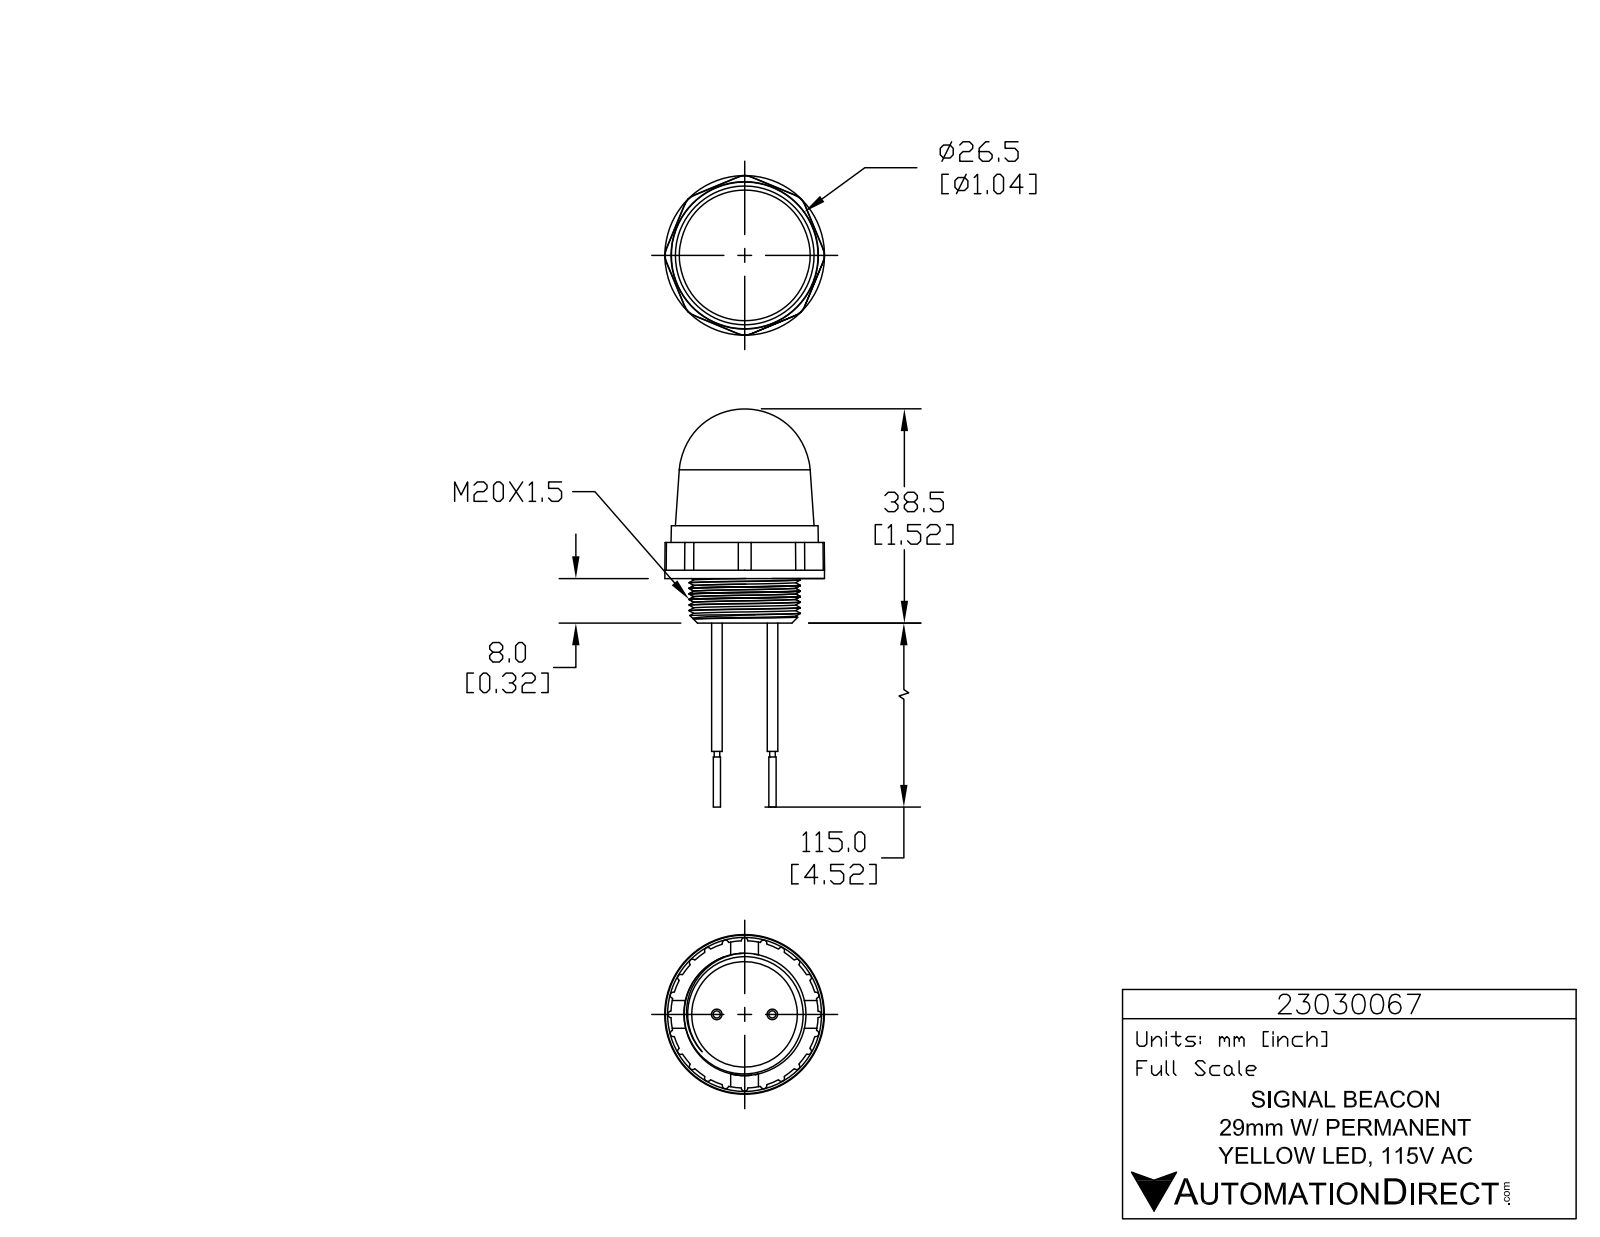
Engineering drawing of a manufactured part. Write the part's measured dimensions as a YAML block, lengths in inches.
part_name: "23030067"
step_written_by: "SolidWorks 2017 (AUTOMOTIVE_DESIGN)"
units: inches
bodies: {solids: 1, faces: 844, planar: 551, cylindrical: 203, other: 90}
overall_size: [2.82, 1.131, 1.131]
volume: 0.978
surface_area: 8.158
round_holes:
  - {diameter: 0.02, count: 3}
  - {diameter: 0.807, count: 1}
round_bosses_or_shafts:
  - {diameter: 0.113, count: 3}
  - {diameter: 0.028, count: 3}
  - {diameter: 0.075, count: 2}
  - {diameter: 0.051, count: 2}
  - {diameter: 0.039, count: 2}
  - {diameter: 1.131, count: 1}
  - {diameter: 1.122, count: 1}
  - {diameter: 0.894, count: 1}
partial_cylinders:
  - {radius: 0.118, count: 8}
  - {radius: 0.004, count: 6}
  - {radius: 0.004, count: 6}
  - {radius: 0.004, count: 6}
  - {radius: 0.065, count: 6}
  - {radius: 0.005, count: 3}
  - {radius: 0.007, count: 3}
  - {radius: 0.008, count: 3}
face_to_face_distances: [0.276, 0.374, 0.039, 0.315, 0.65, 0.638, 0.362, 0.689, 0.413, 0.051]
